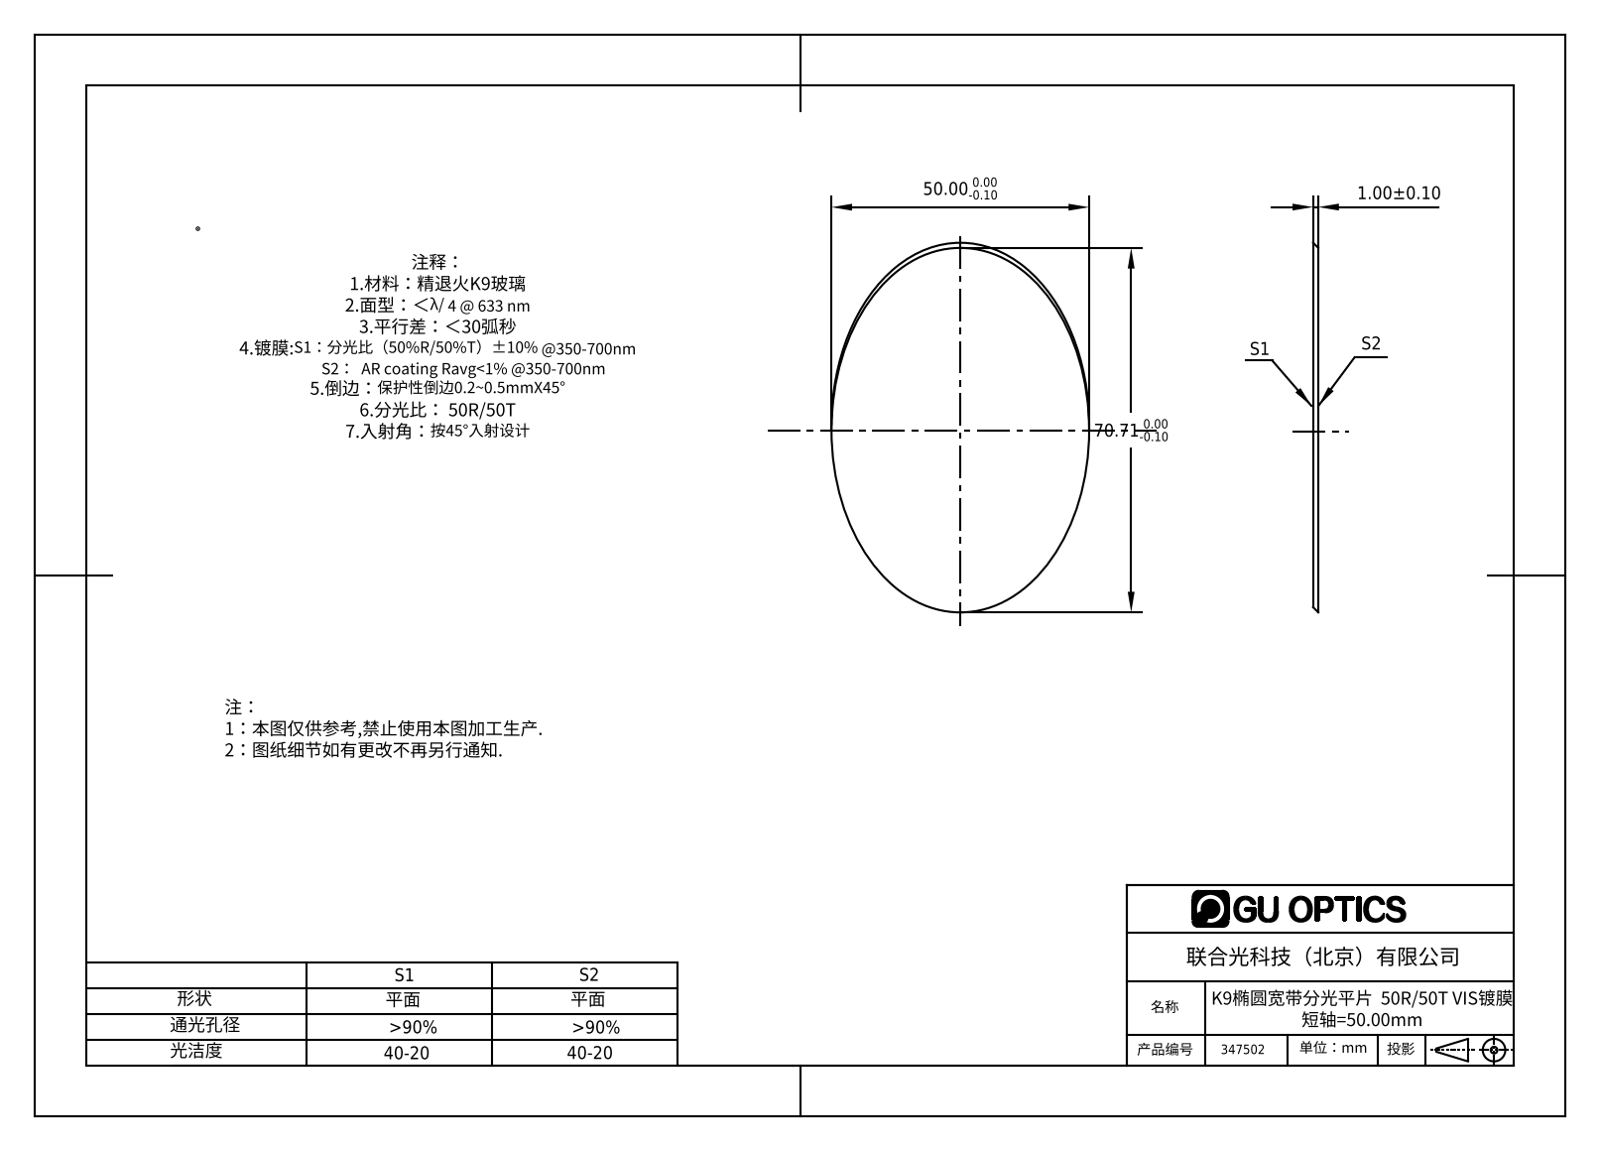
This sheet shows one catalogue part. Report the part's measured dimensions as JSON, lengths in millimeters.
{"part_name": "347502", "step_written_by": "SolidWorks 2019 (CONFIG_CONTROL_DESIGN)", "units": "millimeters", "bodies": {"solids": 1, "faces": 4, "planar": 2, "cylindrical": 2, "other": 0}, "overall_size": [51.41, 50, 50], "volume_mm3": 2777, "surface_area_mm2": 5777, "round_bosses_or_shafts": [[50, 1]], "face_to_face_distances": [1]}
